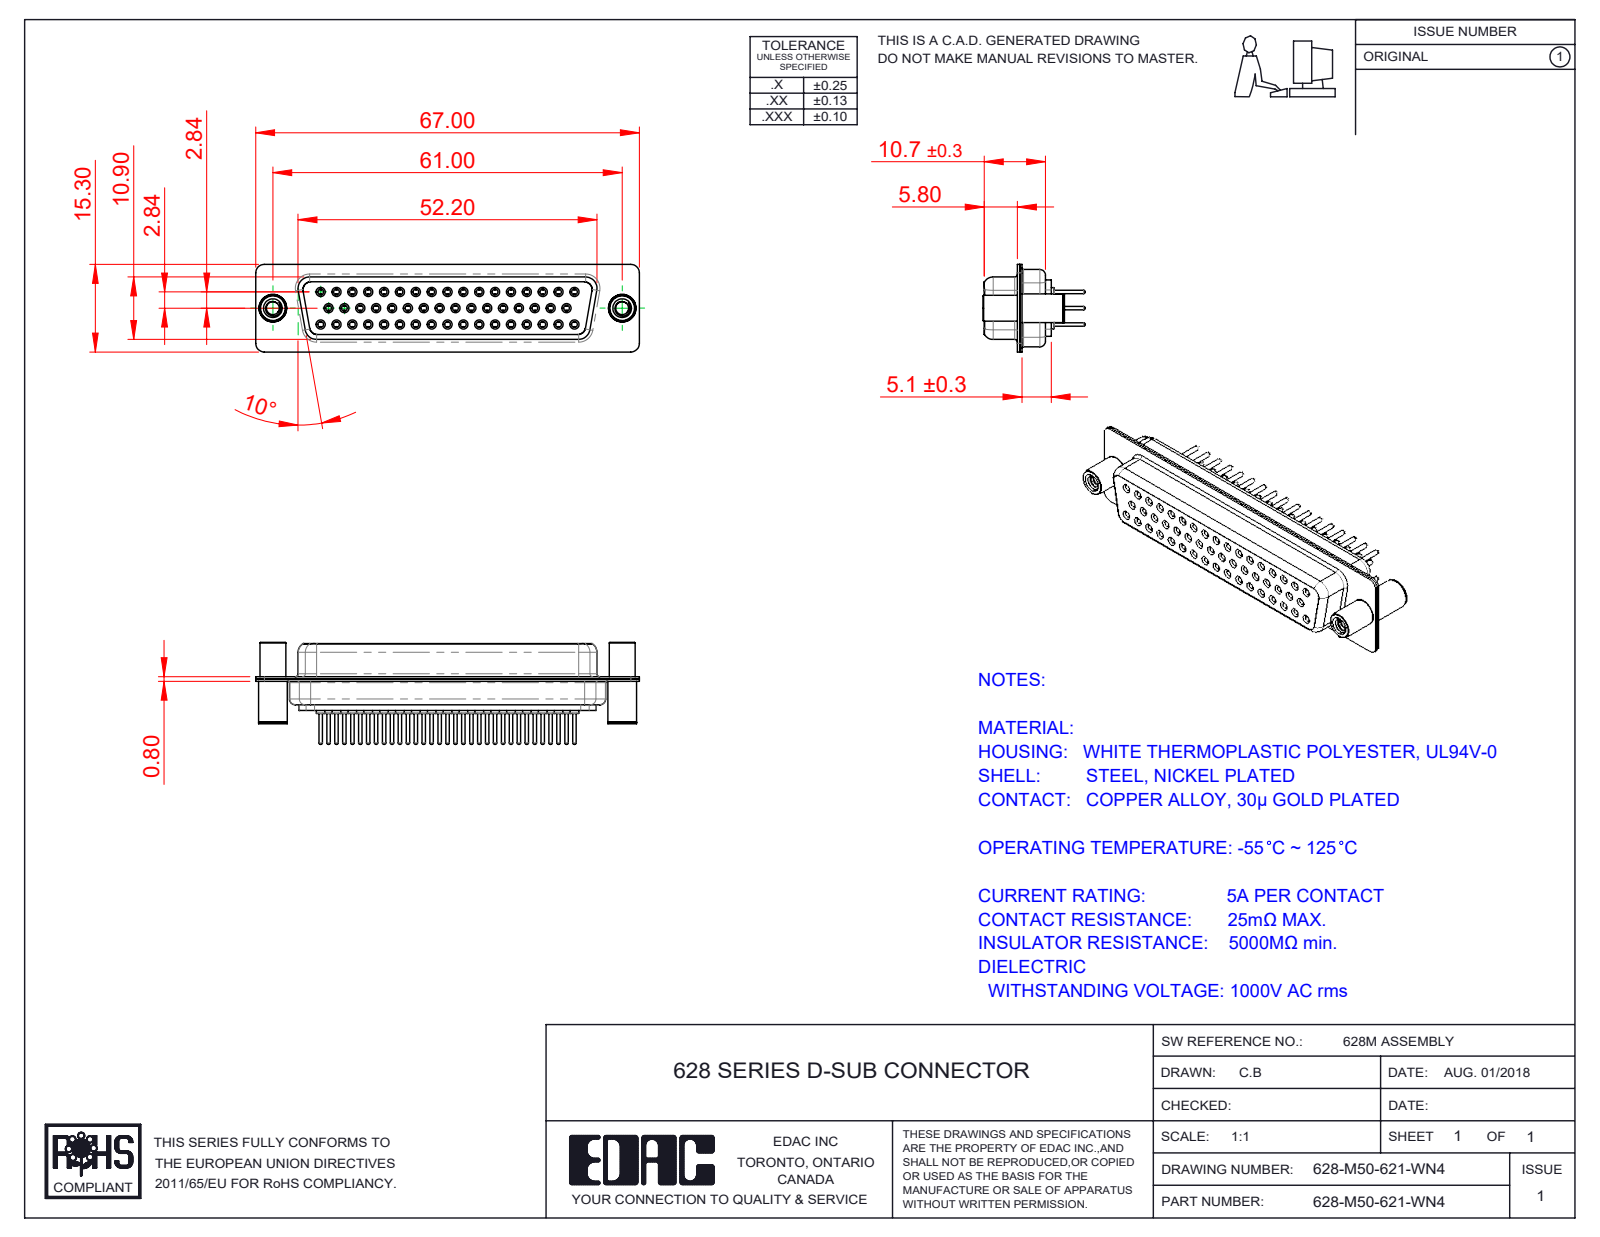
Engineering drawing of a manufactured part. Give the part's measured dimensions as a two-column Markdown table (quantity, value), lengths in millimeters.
| quantity | value |
| --- | --- |
| part name | 628M Contact Row 1_21; 628M 4-40 Threaded Standoff and Board Spacer; 628-M50-621-WN4; 628M Shell Rear_50 Contacts (+4 more) |
| STEP written by | SolidWorks 2020 (CONFIG_CONTROL_DESIGN) |
| units | millimeters |
| bodies | 55 solids, 3115 faces (823 planar, 1139 cylindrical, 1153 other) |
| overall size | 67 × 17.8 × 15.3 |
| volume | 6 909 mm³ |
| surface area | 15 567 mm² |
| round holes (diameter × count) | 1 × 50, 1.1 × 50, 1.7 × 50, 1.8 × 50, 2 × 50, 2.26 × 2, 3.26 × 2, 4 × 2, 4.8 × 2 |
| round bosses / shafts (diameter × count) | 2.2 × 50, 1.6 × 50, 1.5 × 50, 0.6 × 50, 5 × 2, 4.9 × 2, 4.5 × 2 |
| partial cylindrical surfaces (radius × count) | 1.5 × 16, 2 × 12, 1.35 × 8, 1.6 × 8, 0.25 × 4, 0.5 × 4, 0.6 × 4, 0.65 × 4 |
| main face-to-face distances | 0.4, 1.3, 11.8, 0.9, 5.5, 5.9, 0.85, 13.1, 5.8, 10.5 |
| hole center spacings | 3.16, 2.77, 5.54, 8.31, 11.08, 13.85, 16.62, 19.39 |
